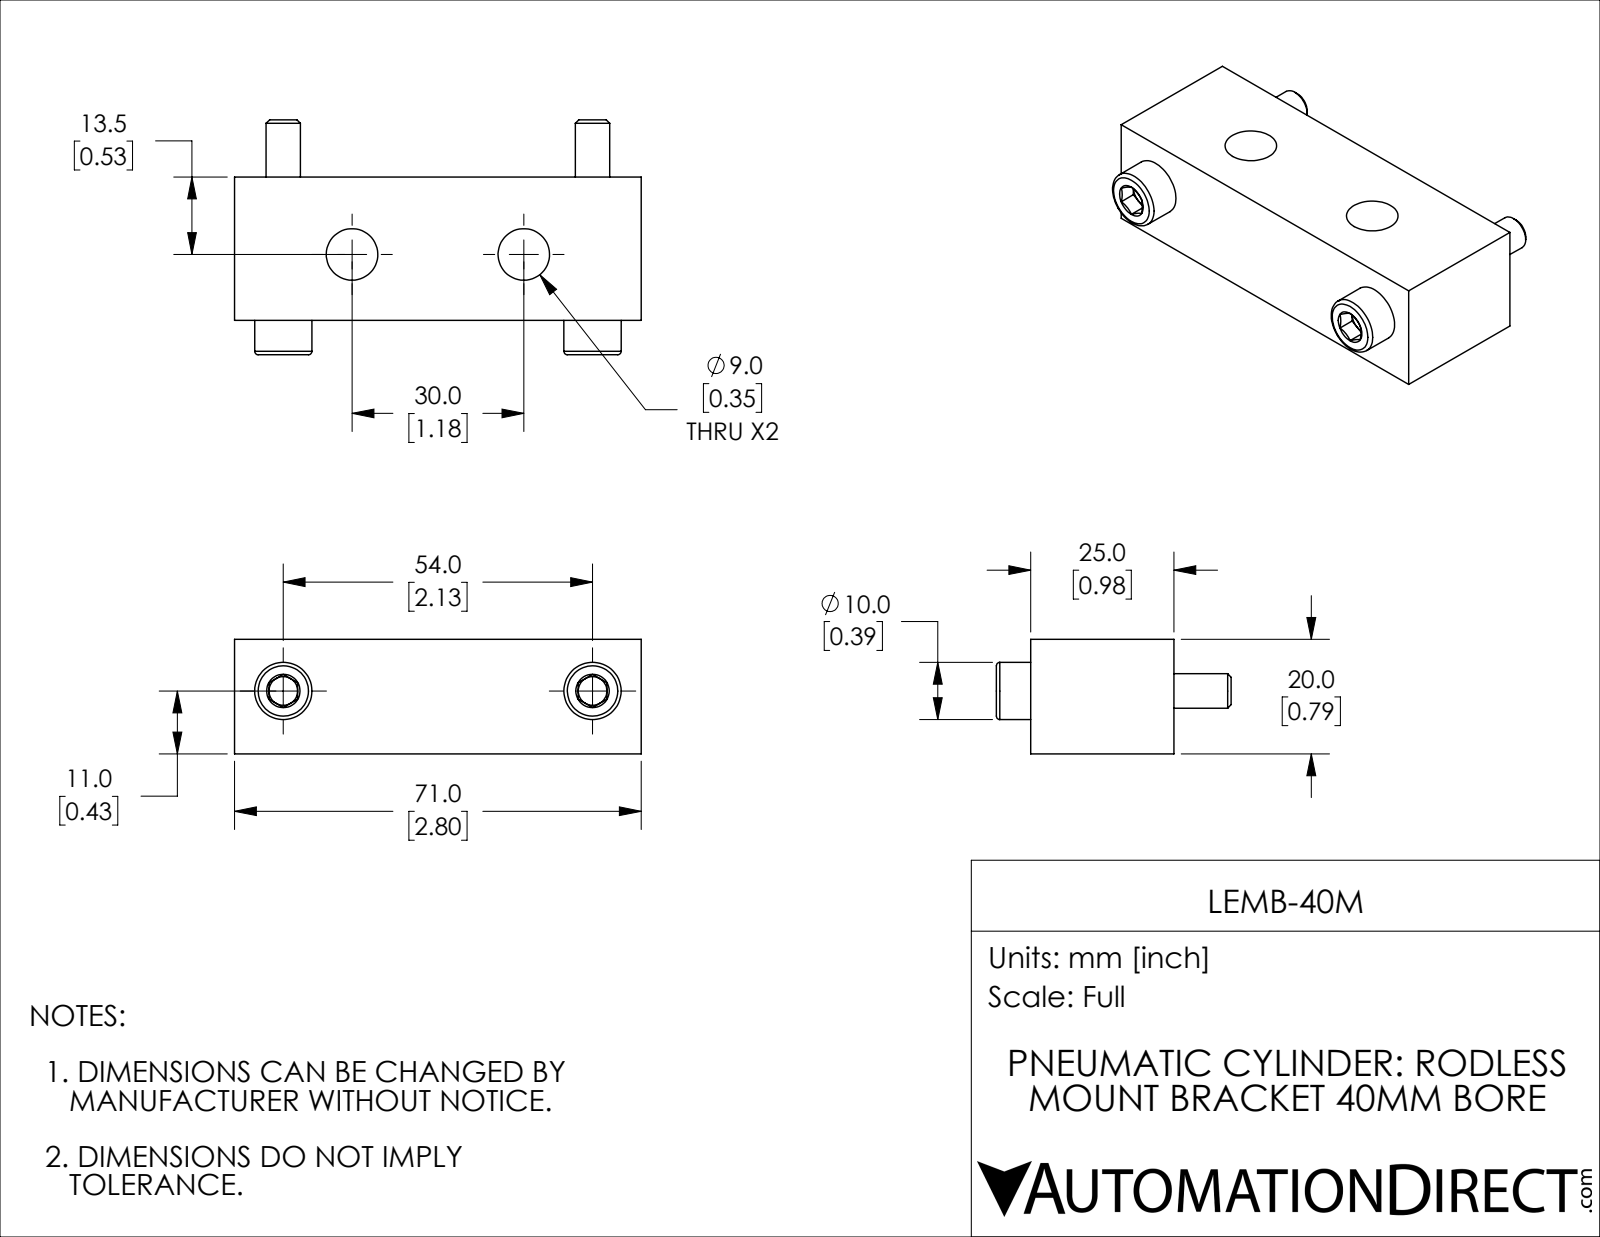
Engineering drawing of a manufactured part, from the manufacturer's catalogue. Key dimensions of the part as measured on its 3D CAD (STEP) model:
Part name (STEP PRODUCT): LEMB-40M
STEP written by: SolidWorks 2019 (CONFIG_CONTROL_DESIGN)
Units: inches
Bodies: 3 solids, 80 faces (36 planar, 16 cylindrical, 28 other)
Overall size (bounding box): 2.795 × 1.614 × 0.787
Volume: 2.093 in³ · Surface area: 17.32 in²
Round holes (diameter × count): ⌀0.236 ×2, ⌀0.354 ×2
Round bosses / shafts (diameter × count): ⌀0.394 ×2
Main face-to-face distances: 0.787, 0.984, 2.795, 0.236, 1.22, 0.197, 0.394, 1.378, 1.614, 1.063
Hole centre spacings: 1.181, 2.126
